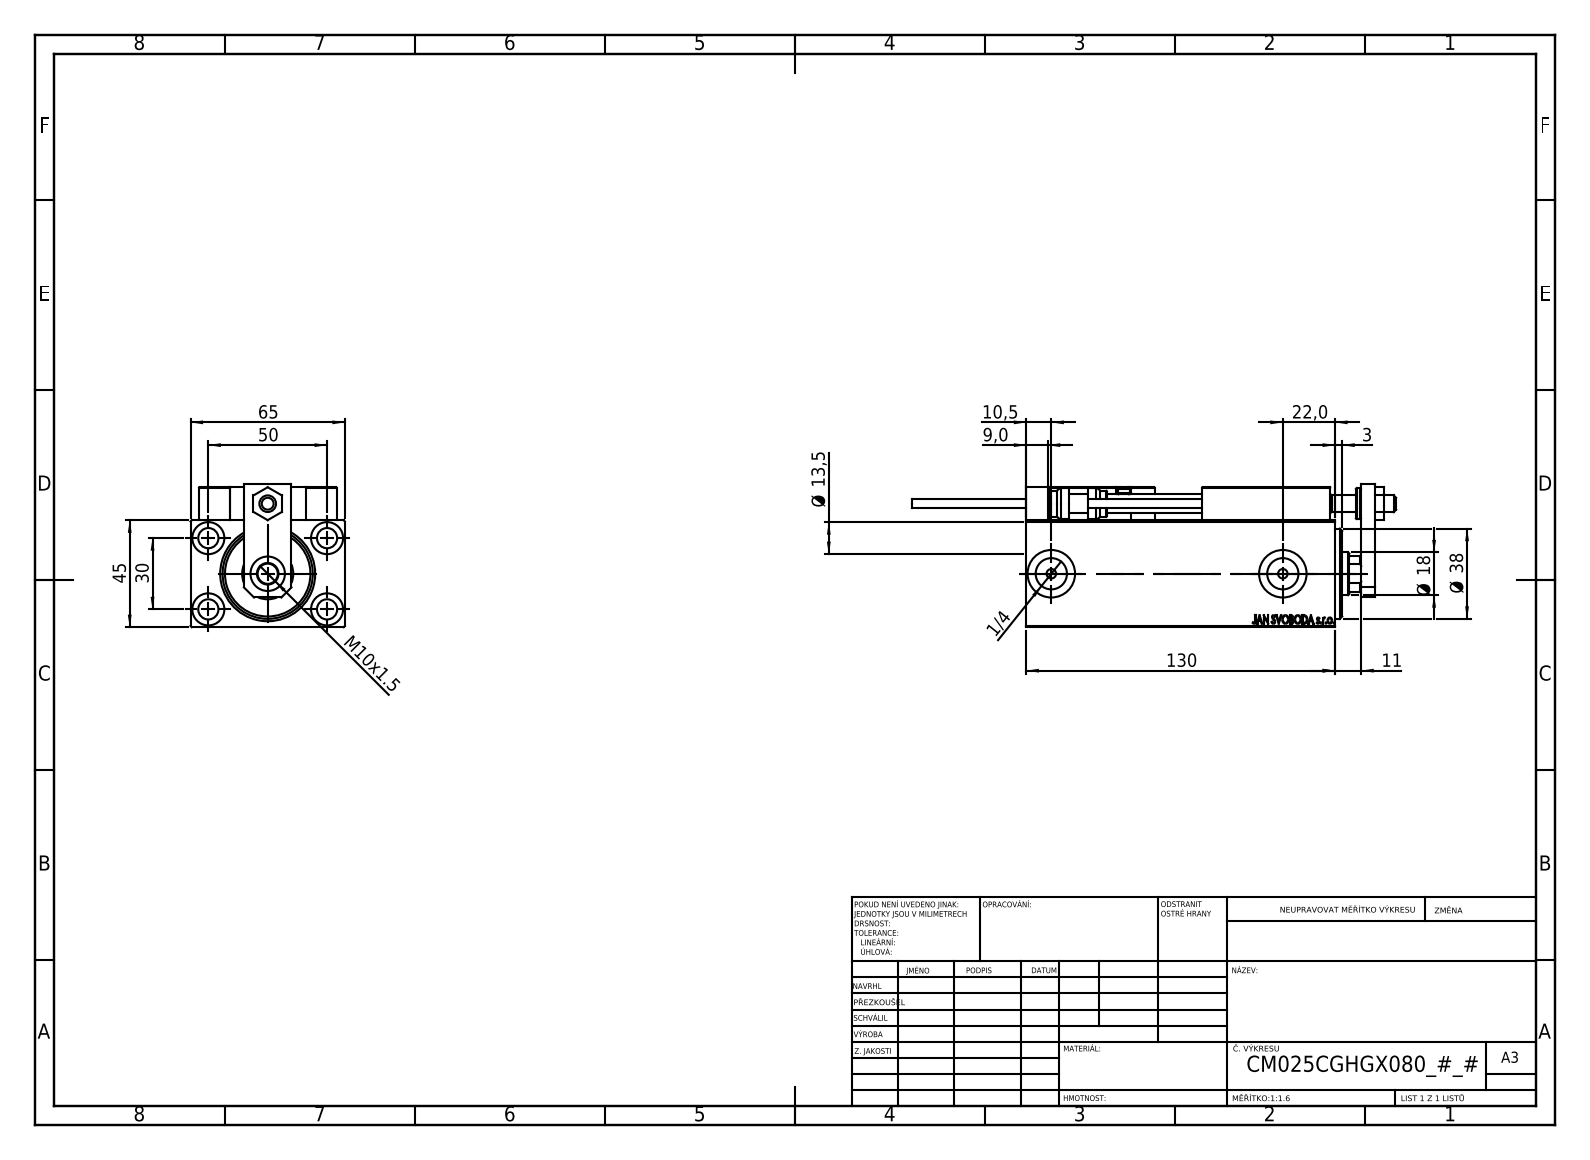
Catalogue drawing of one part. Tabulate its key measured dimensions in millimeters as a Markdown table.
| quantity | value |
| --- | --- |
| part name | V450CM_C_Body; ZARAZKA; SWITCH_X_FRONT_BACK; SWITCH DIM B,W (+7 more) |
| STEP written by | SolidWorks 2019 (CONFIG_CONTROL_DESIGN) |
| units | millimeters |
| bodies | 23 solids, 1282 faces (560 planar, 188 cylindrical, 534 other) |
| overall size | 203.7 × 65 × 60.5 |
| volume | 373 793 mm³ |
| surface area | 98 342 mm² |
| round holes (diameter × count) | 4 × 6, 8 × 5, 8.5 × 5, 3.2 × 4, 13.5 × 4, 5 × 2, 13.16 × 2, 20 × 2, 7 × 1, 14.5 × 1, 18 × 1, 21.5 × 1 |
| round bosses / shafts (diameter × count) | 5 × 2, 3.8 × 2, 13 × 1, 11 × 1 |
| partial cylindrical surfaces (radius × count) | 0.3 × 30, 3 × 2, 8.5 × 1 |
| main face-to-face distances | 45, 65, 14, 6, 59, 3, 13, 3.5, 7, 20 |
| hole center spacings | 29.15, 11.37, 20, 28.9, 29.59, 29.69, 30, 36.06 |
